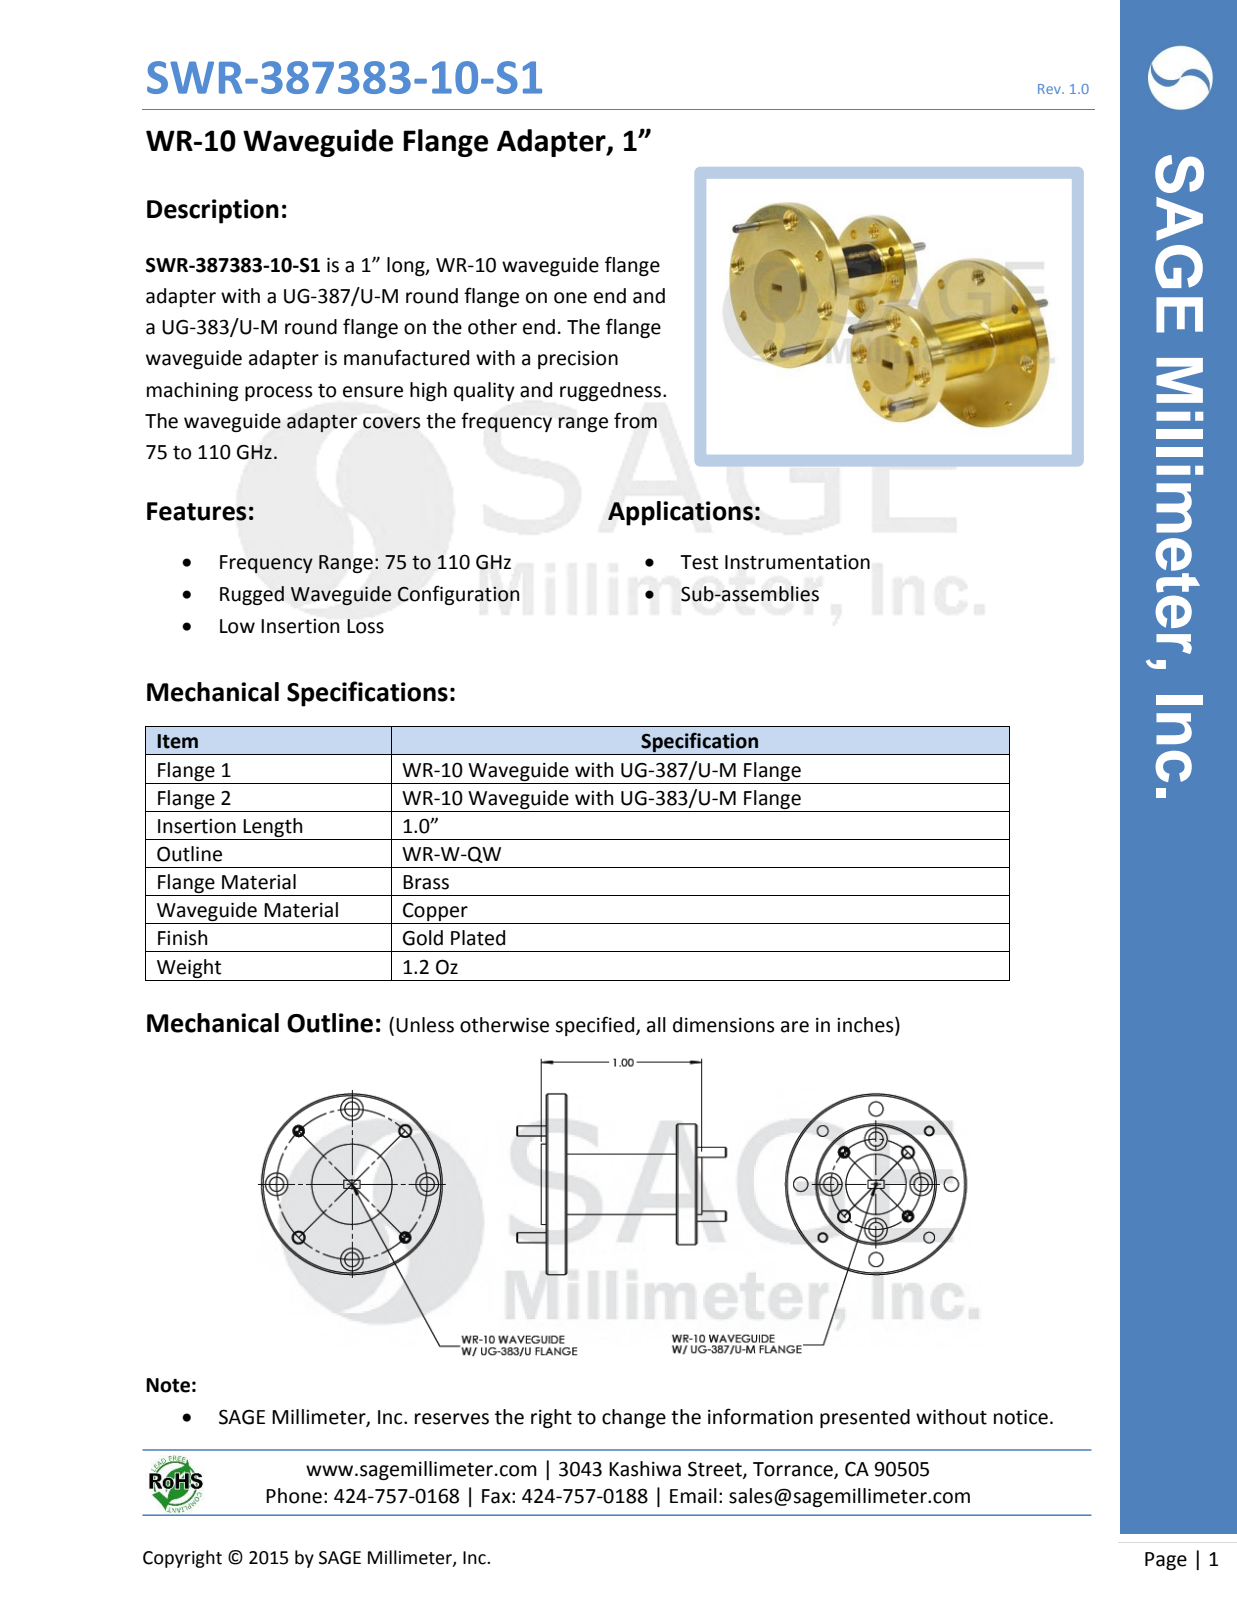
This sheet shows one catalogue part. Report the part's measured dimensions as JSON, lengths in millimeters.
{"part_name": "DMWR-10-401-1", "step_written_by": "SolidWorks 2013 (CONFIG_CONTROL_DESIGN)", "units": "millimeters", "bodies": {"solids": 5, "faces": 132, "planar": 26, "cylindrical": 66, "other": 40}, "overall_size": [33.1, 28.6, 28.6], "volume_mm3": 4230, "surface_area_mm2": 3324, "round_holes": [[2.3, 8], [3.6, 8], [1.5, 4], [1.7, 4]], "round_bosses_or_shafts": [[1.6, 4], [28.6, 1], [19.1, 1], [12.7, 1], [9.5, 1], [9.5, 1]], "face_to_face_distances": [3.3, 0.8, 24.6, 20.6, 17.3, 23.9, 20.6, 3.3, 4.1, 21.3], "hole_center_spacings": [8.5, 13.9, 5.5, 9.1, 17.7, 17.7, 19.1, 22]}
